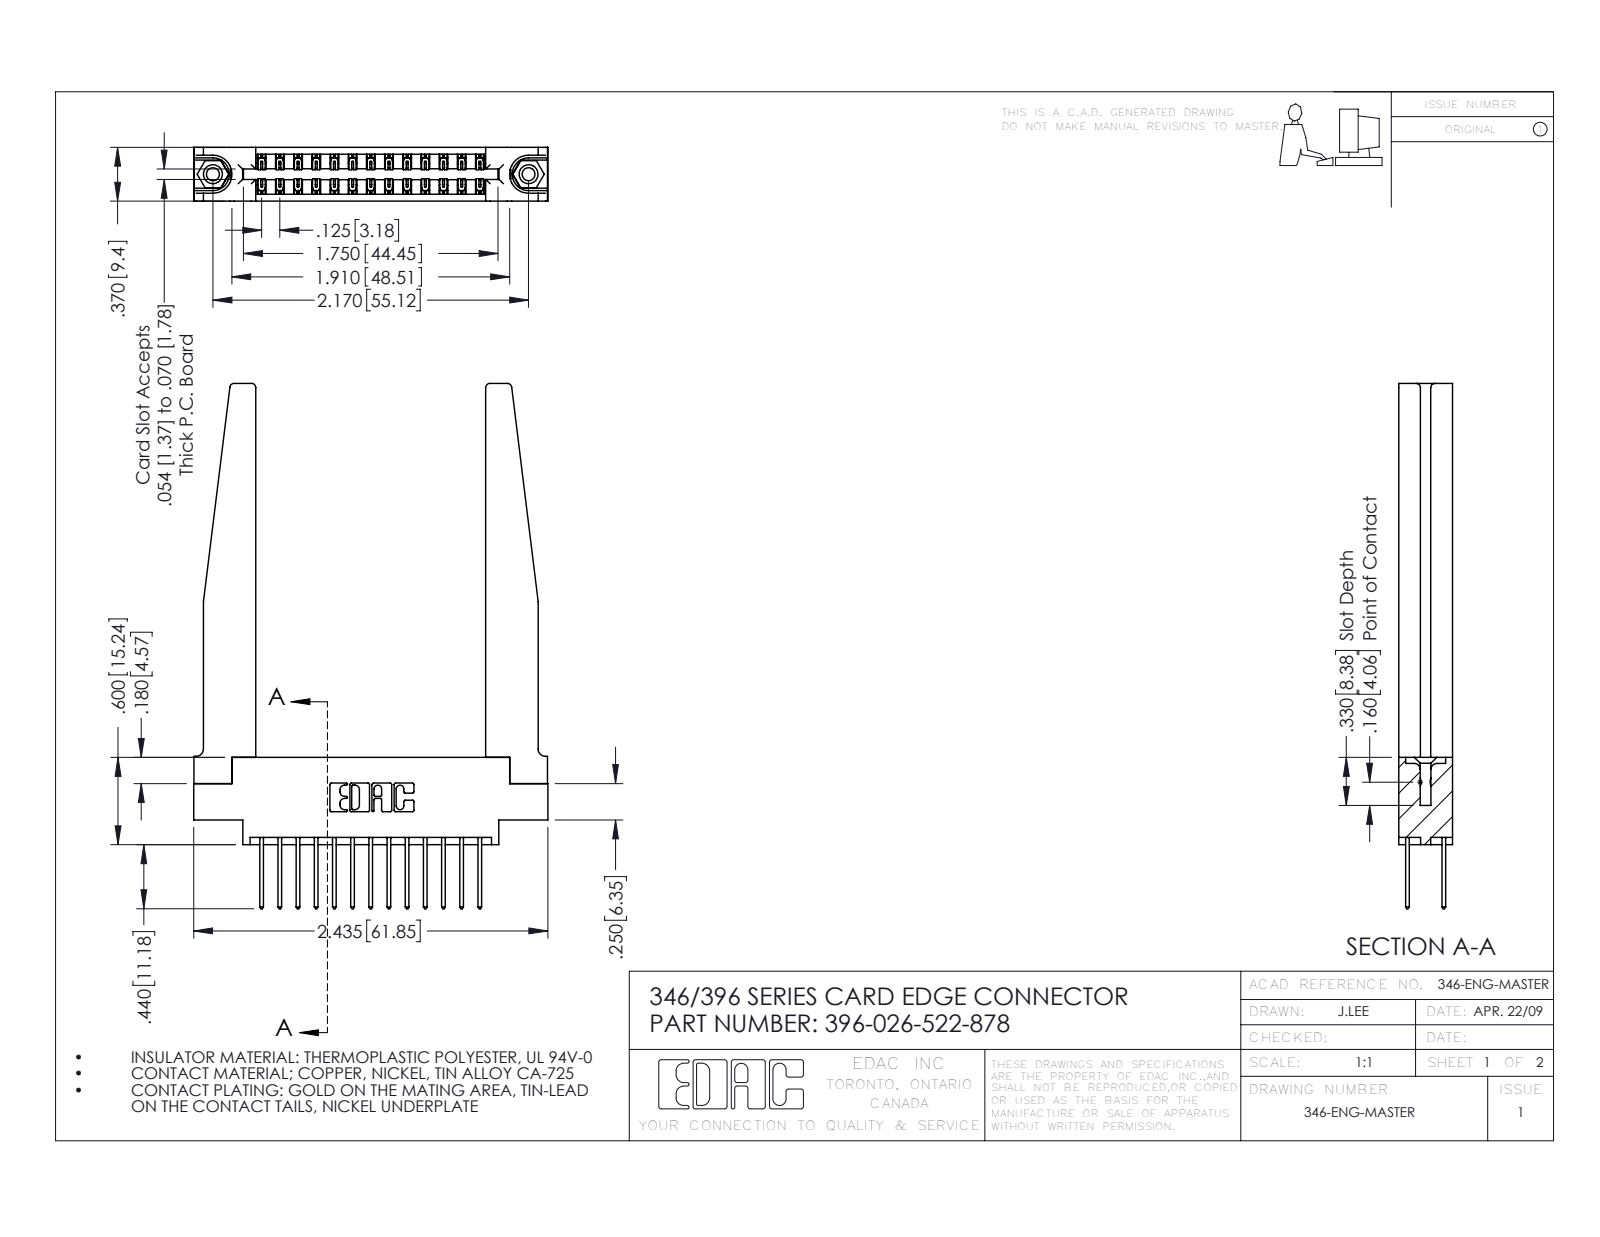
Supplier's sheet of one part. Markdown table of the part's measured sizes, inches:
| quantity | value |
| --- | --- |
| part name | 396-026-522-878; 346-220-078_345-220-078; 346 Part_0.170 Offset - 0.156 Dia-TH; 345-250-001_345-250-001-102 (+1 more) |
| STEP written by | SolidWorks 2016 (CONFIG_CONTROL_DESIGN) |
| units | inches |
| bodies | 31 solids, 1712 faces (1132 planar, 528 cylindrical, 52 other) |
| overall size | 3.61 × 2.435 × 0.37 |
| volume | 0.771 in³ |
| surface area | 22.37 in² |
| round holes (diameter × count) | 0.089 × 2, 0.125 × 2, 0.156 × 2, 0.064 × 1 |
| round bosses / shafts (diameter × count) | 0.155 × 2 |
| partial cylindrical surfaces (radius × count) | 0.006 × 39, 0.01 × 26, 0.01 × 22, 0.03 × 8, 0.007 × 6, 0.031 × 6, 0.026 × 3, 0.014 × 2 |
| main face-to-face distances | 0.37, 0.072, 0.048, 0.322, 0.148, 0.15, 0.25, 0.298, 0.025, 0.102 |
| hole center spacings | 0.246, 1.964, 2.17 |
